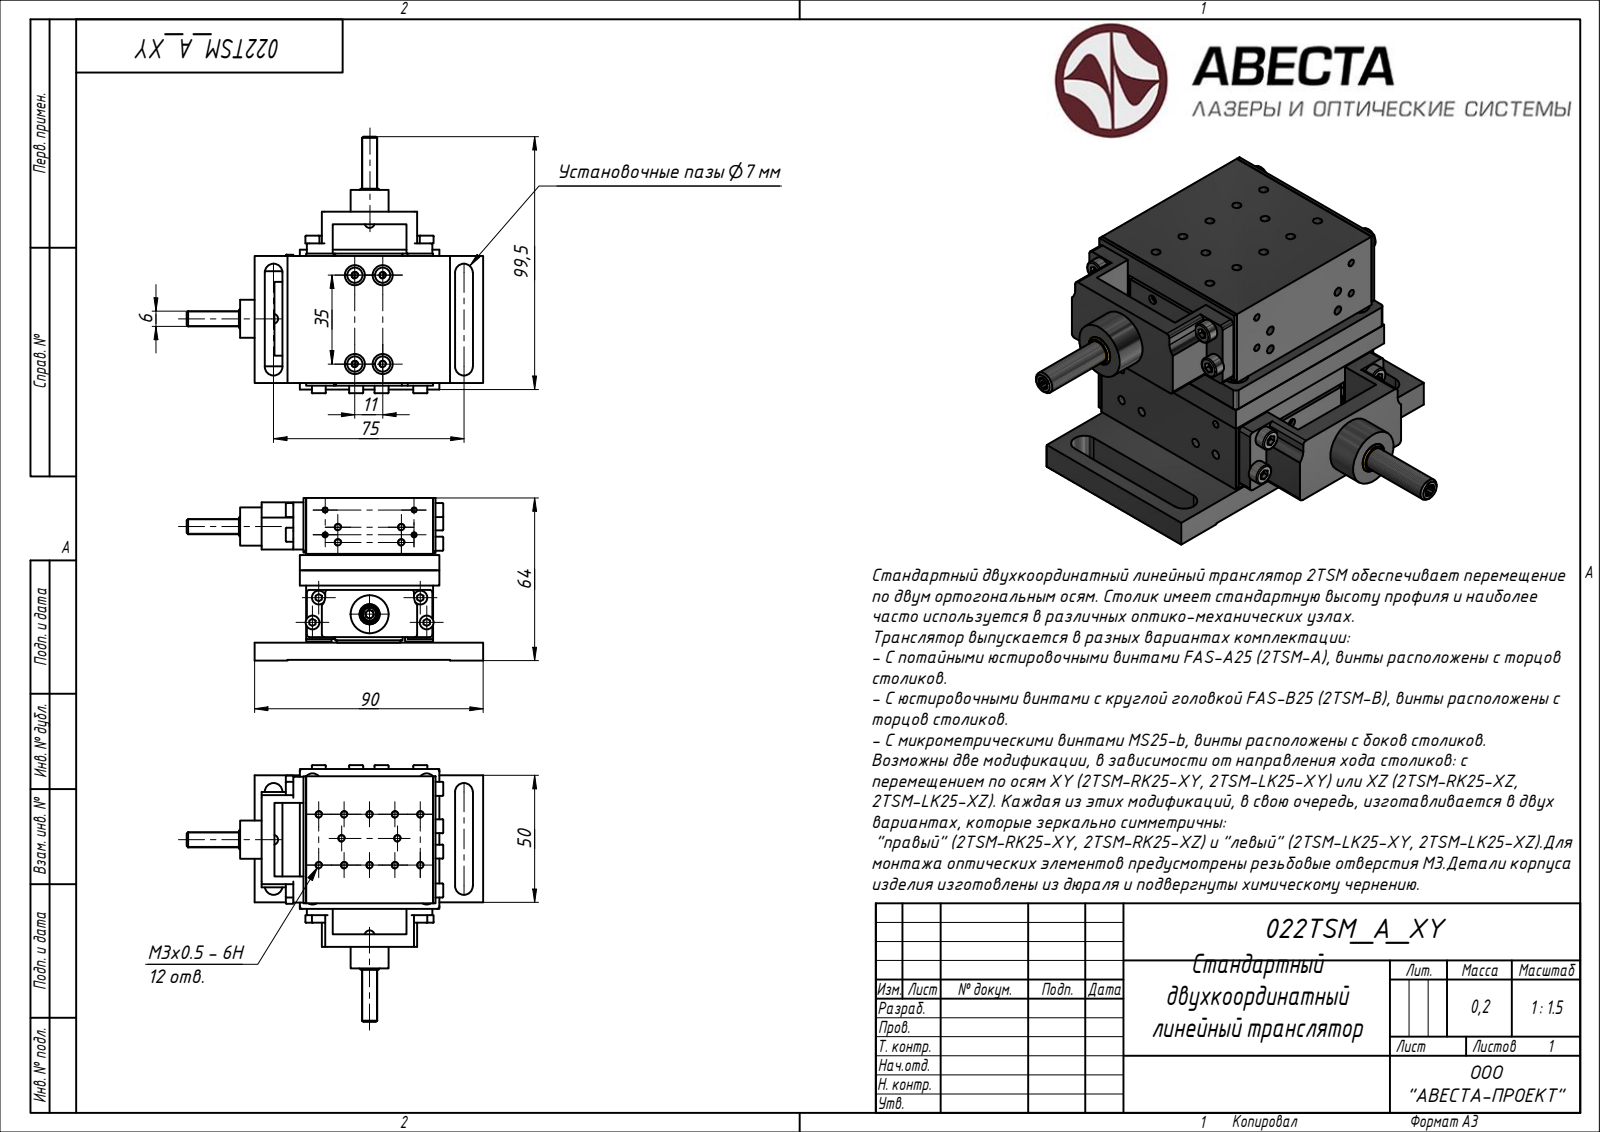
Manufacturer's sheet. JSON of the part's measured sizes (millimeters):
{"step_written_by": "ST-DEVELOPER v15 (AUTOMOTIVE_DESIGN)", "units": "millimeters", "bodies": {"solids": 24, "faces": 1184, "planar": 0, "cylindrical": 0, "other": 1184}, "overall_size": [116.7, 100, 64]}
